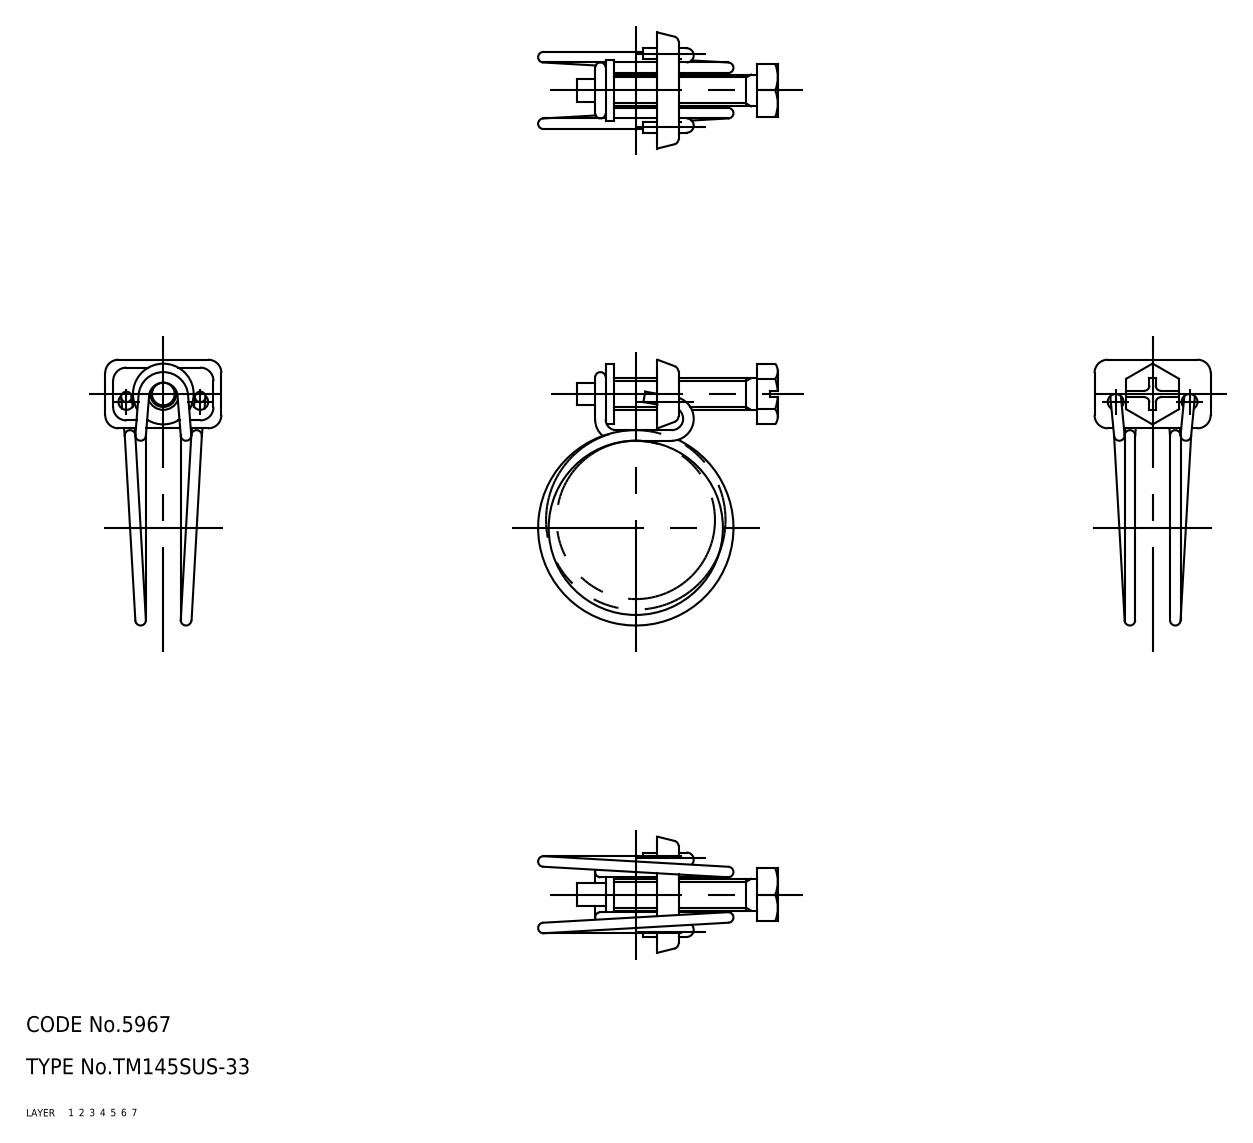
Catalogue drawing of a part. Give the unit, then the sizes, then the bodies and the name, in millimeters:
Units: millimetres
Overall size (bounding box): 50.35 × 45.4 × 22
Volume: 2 767 mm³ · Surface area: 3 847 mm²
Bodies: 3 solids, 119 faces (0 planar, 0 cylindrical, 119 other)
Part name (STEP PRODUCT): screw; holder; band; TM_145SUS_33_21978_36
STEP written by: CADfix (AUTOMOTIVE_DESIGN)
